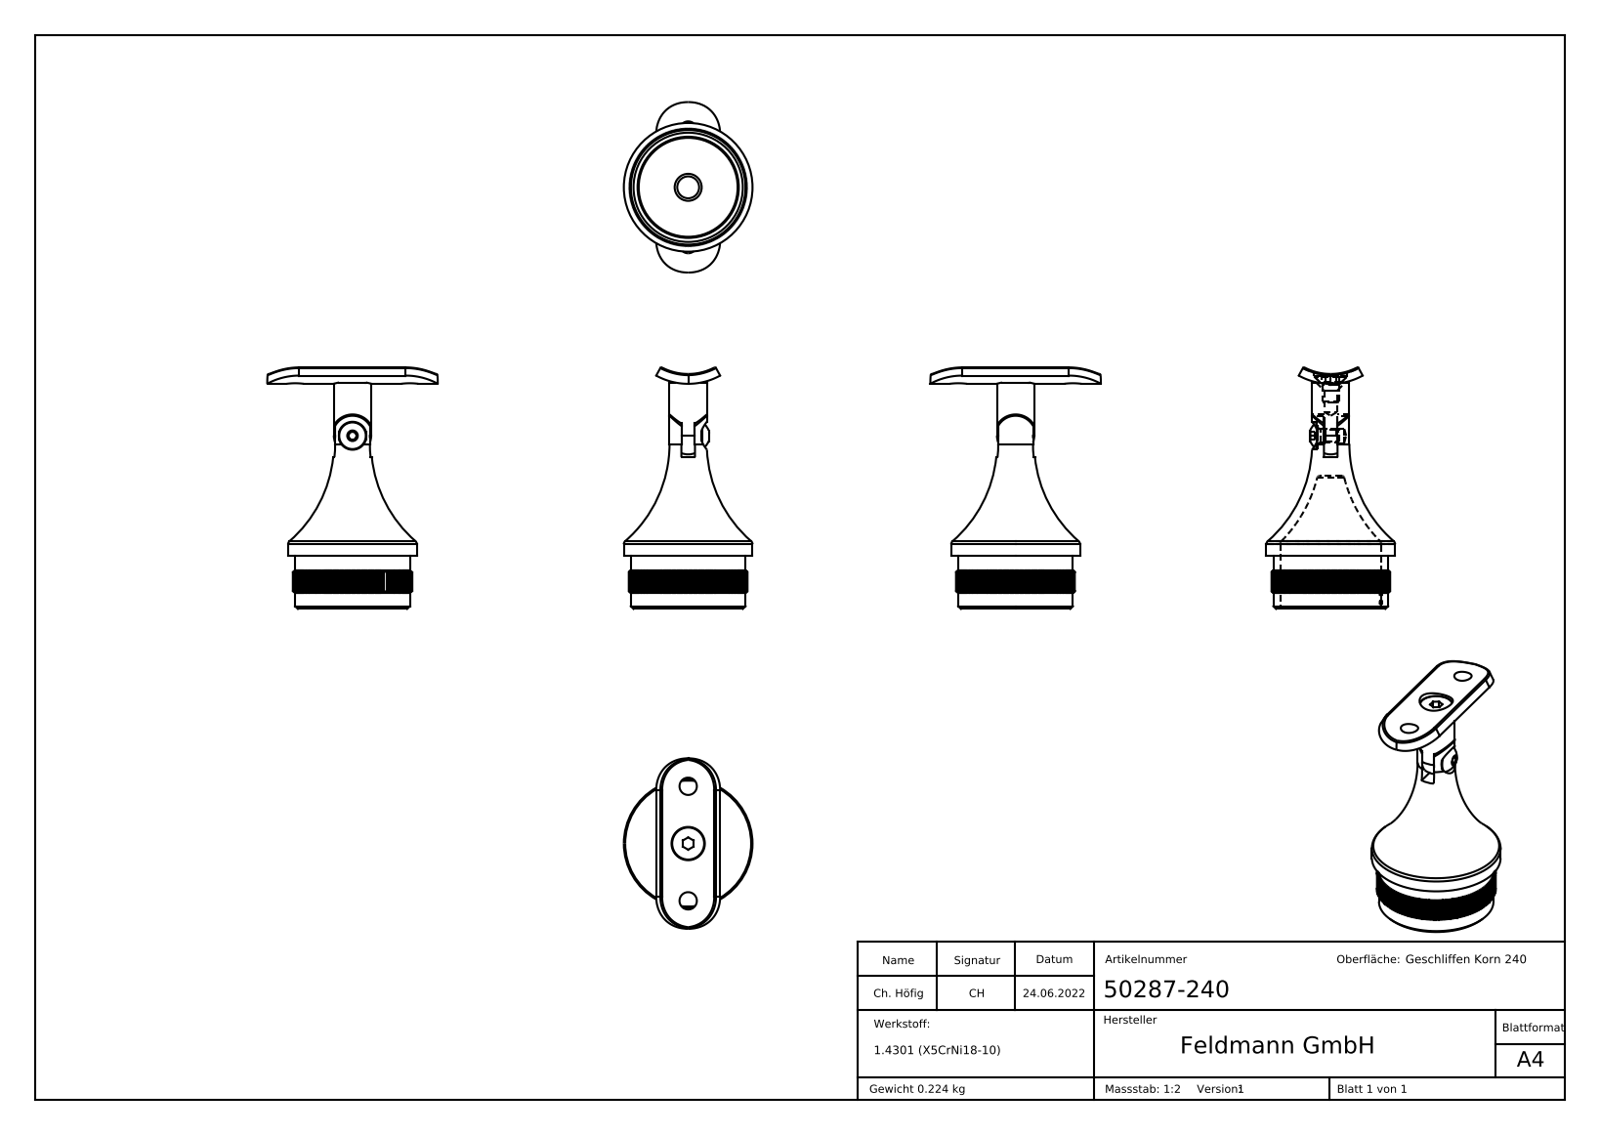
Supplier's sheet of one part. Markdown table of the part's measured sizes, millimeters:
| quantity | value |
| --- | --- |
| part name | 5028x-240 Teil2_5028x-240 Teil2; DIN 7991 Konfig_DIN 7991 M6x10; DIN 7380_DIN 7380 M5x8; 50287-240 (+2 more) |
| STEP written by | SolidWorks 2018 (CONFIG_CONTROL_DESIGN) |
| units | millimeters |
| bodies | 5 solids, 1116 faces (448 planar, 215 cylindrical, 453 other) |
| overall size | 90.65 × 64 × 48.3 |
| volume | 28 400 mm³ |
| surface area | 19 999 mm² |
| round holes (diameter × count) | 6.5 × 2, 4.2 × 1, 5 × 1, 5.5 × 1, 8.1 × 1, 10.5 × 1, 12.5 × 1, 38 × 1 |
| round bosses / shafts (diameter × count) | 48.3 × 1, 43 × 1, 14 × 1, 12 × 1, 10 × 1, 6 × 1, 5 × 1 |
| partial cylindrical surfaces (radius × count) | 12 × 4, 0.5 × 2, 7.1 × 1, 7.5 × 1, 8 × 1, 19.1 × 1, 21.2 × 1, 22.27 × 1 |
| main face-to-face distances | 21.5, 21.51, 5.05, 21.52, 21.49, 2.35, 21.48, 20, 5.1, 5 |
| hole center spacings | 21.5, 43 |
